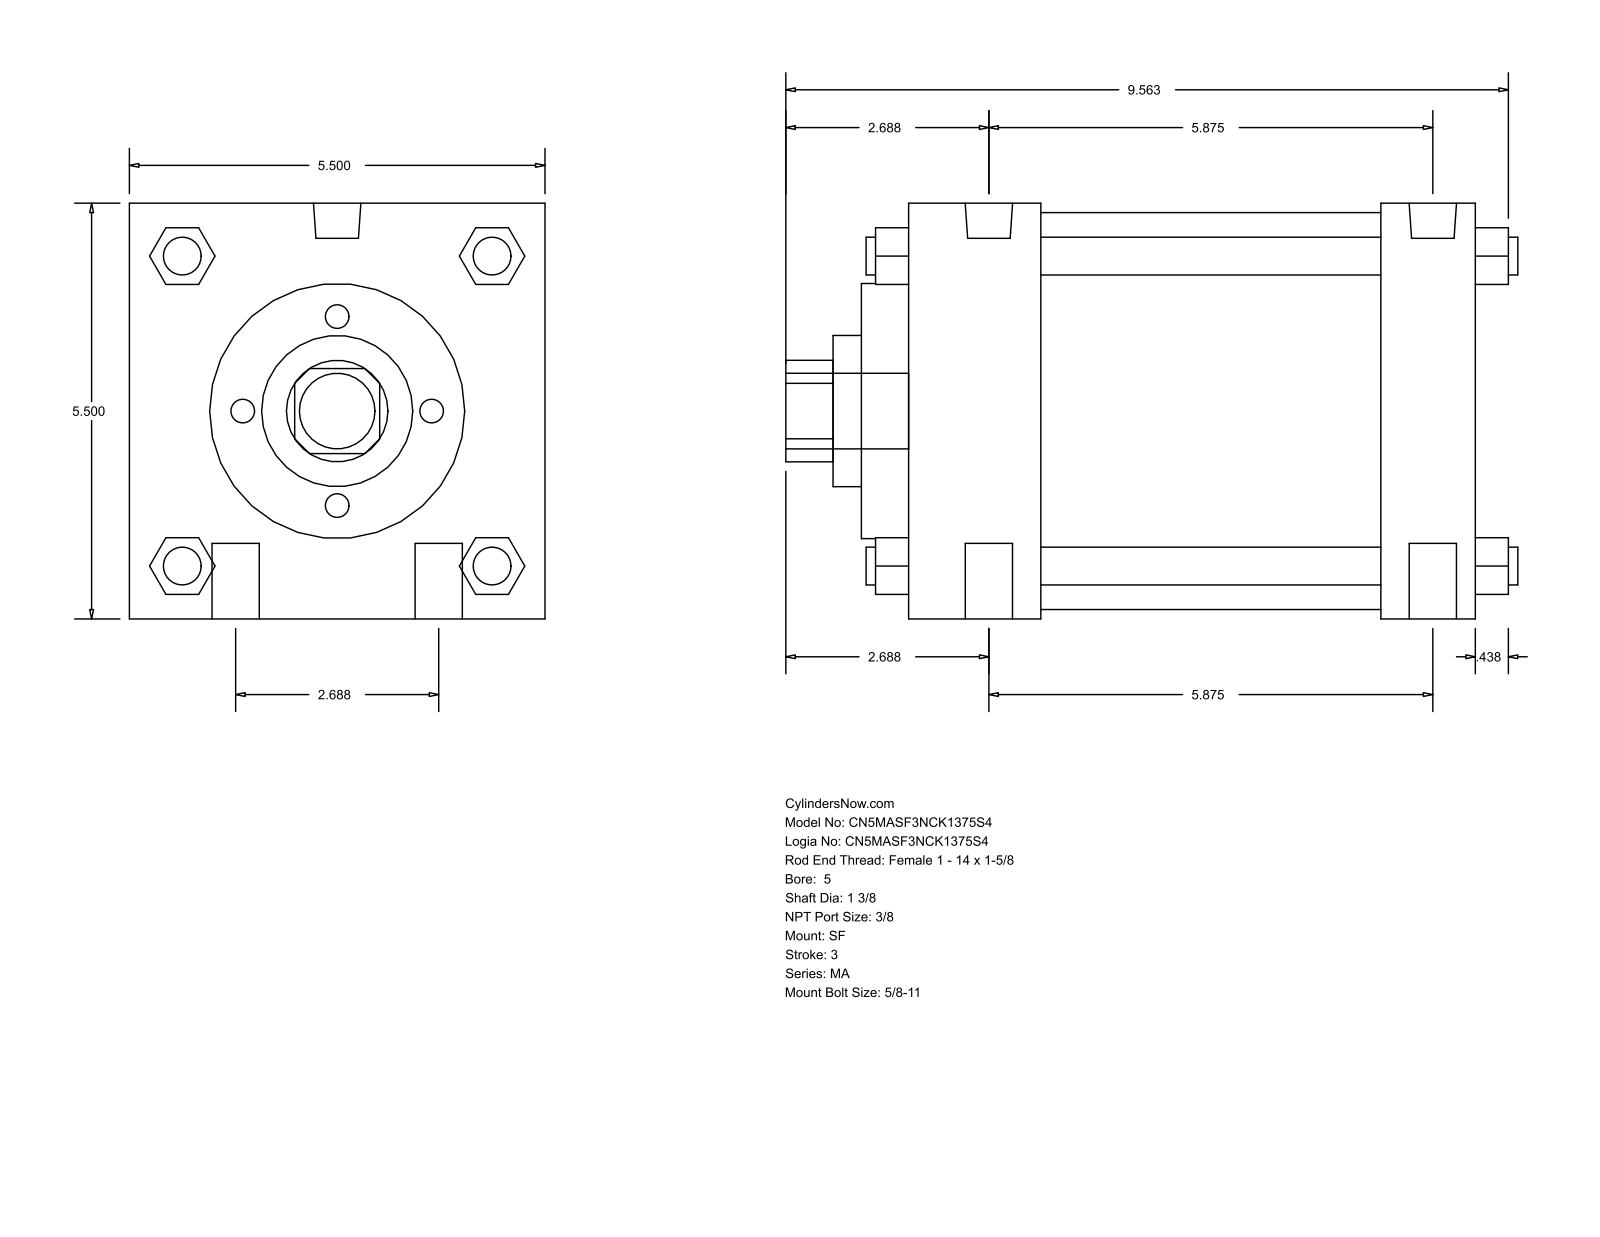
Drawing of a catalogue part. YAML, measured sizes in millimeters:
part_name: "MA_SF__0500_1.375"
step_written_by: "GSSL Pune (CONFIG_CONTROL_DESIGN)"
units: millimeters
bodies: {solids: 0, faces: 126, planar: 95, cylindrical: 31, other: 0}
overall_size: [246.06, 139.7, 139.7]
round_holes:
  - {diameter: 34.92, count: 1}
  - {diameter: 50.8, count: 1}
  - {diameter: 85.72, count: 1}
  - {diameter: 133.35, count: 1}
round_bosses_or_shafts:
  - {diameter: 15.88, count: 4}
  - {diameter: 12.7, count: 4}
  - {diameter: 15.93, count: 2}
  - {diameter: 11.11, count: 2}
  - {diameter: 25.4, count: 1}
partial_cylinders:
  - {radius: 17.06, count: 1}
face_to_face_distances: [139.7, 190.51, 44.45, 158.76, 114.31, 146.06, 31.75, 15.87, 60.32, 174.63]
